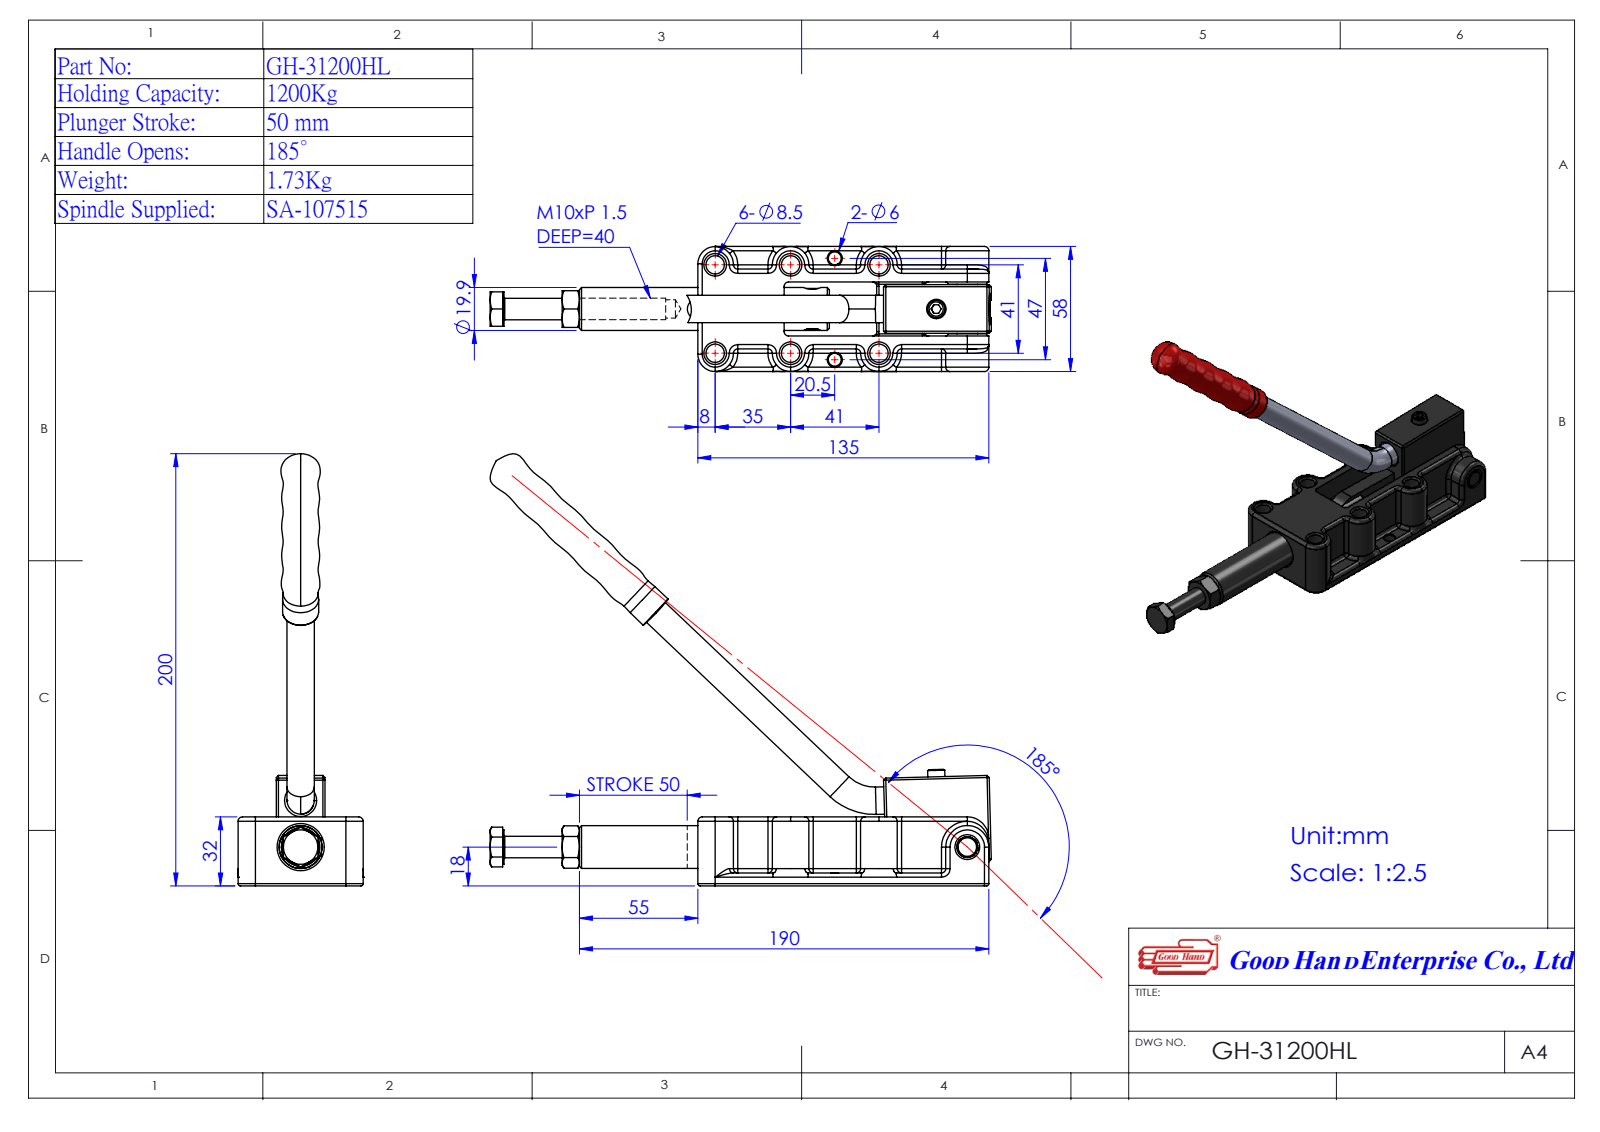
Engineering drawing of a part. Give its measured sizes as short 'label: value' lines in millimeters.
name: Group5^GH-31200HL(簡化)-1; Group1^GH-31200HL(簡化); Group4^GH-31200HL(簡化)-1; GH-31200HL(簡化)-1 (+2 more)
written by: SolidWorks 2016 (AUTOMOTIVE_DESIGN)
unit: mm
bodies: 5 solids, 311 faces (90 planar, 114 cylindrical, 107 other)
size: 247.51 × 195.44 × 64.6
volume: 236 340 mm³; area: 75 968 mm²
holes: 7× ⌀8.5, 4× ⌀6, 1× ⌀8, 1× ⌀19.9
bosses: 2× ⌀12.7, 1× ⌀16, 1× ⌀14.7, 1× ⌀10, 1× ⌀8
rounds: 30× R2, 6× R8.5, 2× R8, 2× R10, 2× R11, 1× R9
face distances: 1.2, 23.8, 6, 25, 7.2, 29.8, 31, 32, 22.6, 14.45
hole spacings: 41, 20.72, 48.54, 35, 53.91, 55.58, 57.98, 70.83
